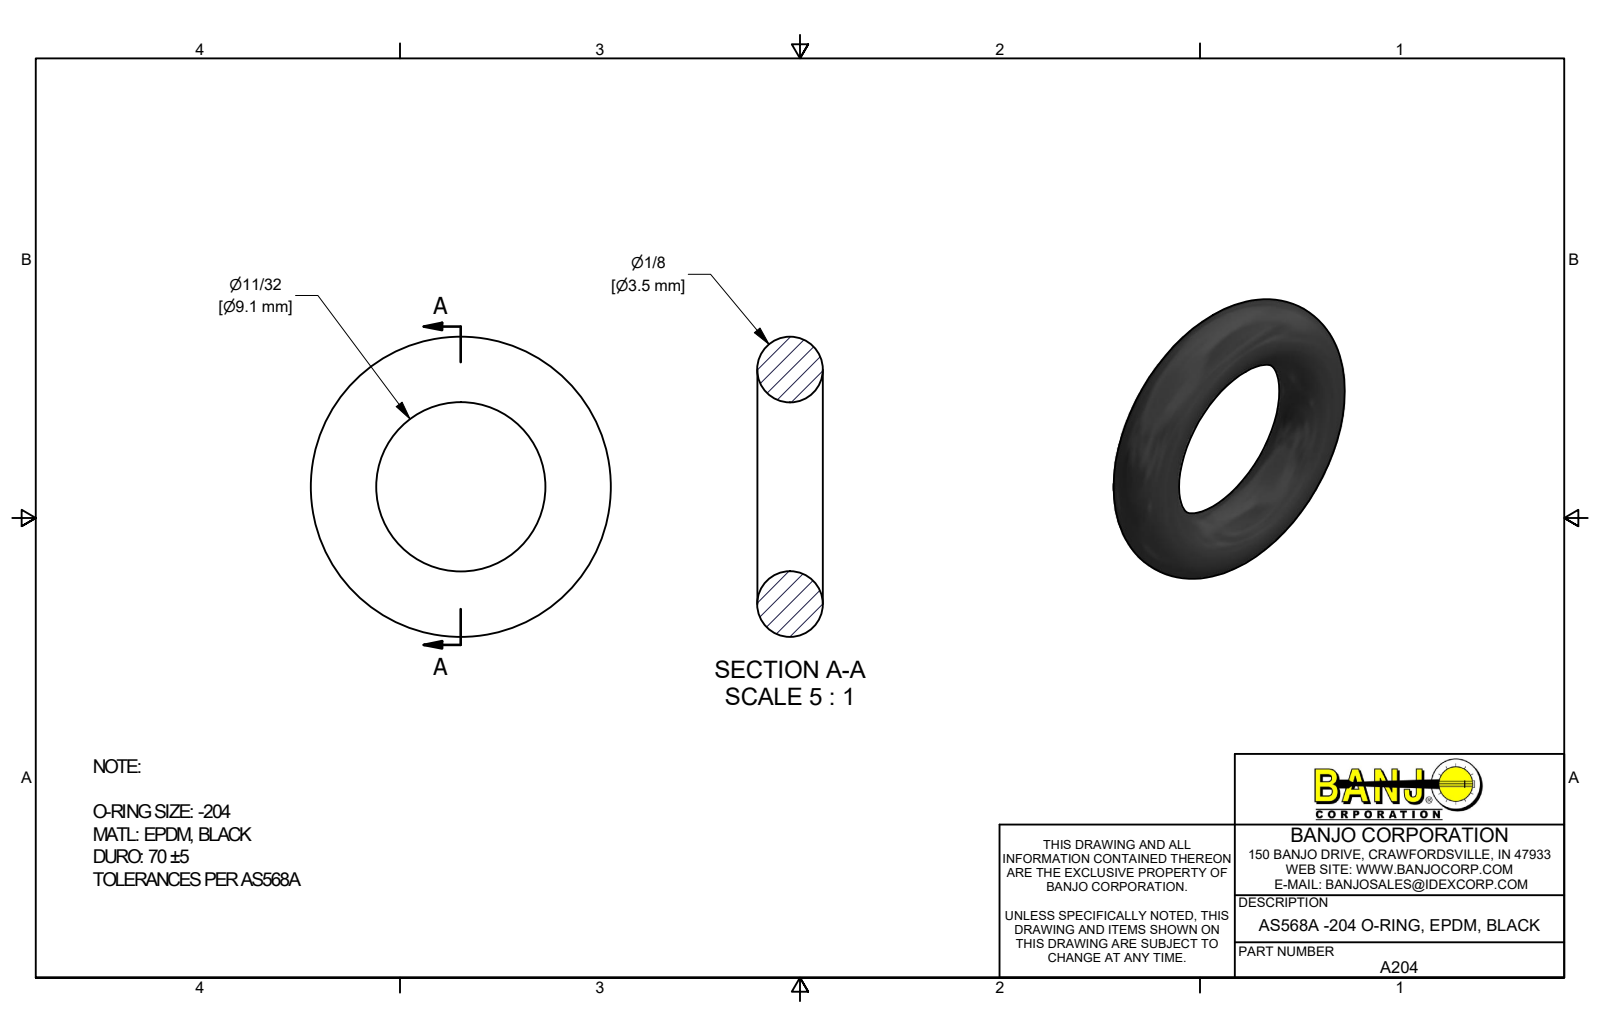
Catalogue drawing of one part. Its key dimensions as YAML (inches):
part_name: "A204"
step_written_by: "Autodesk Inventor 2019 (AUTOMOTIVE_DESIGN)"
units: inches
bodies: {solids: 1, faces: 1, planar: 0, cylindrical: 0, other: 1}
overall_size: [0.637, 0.637, 0.139]
volume: 0.024
surface_area: 0.683
